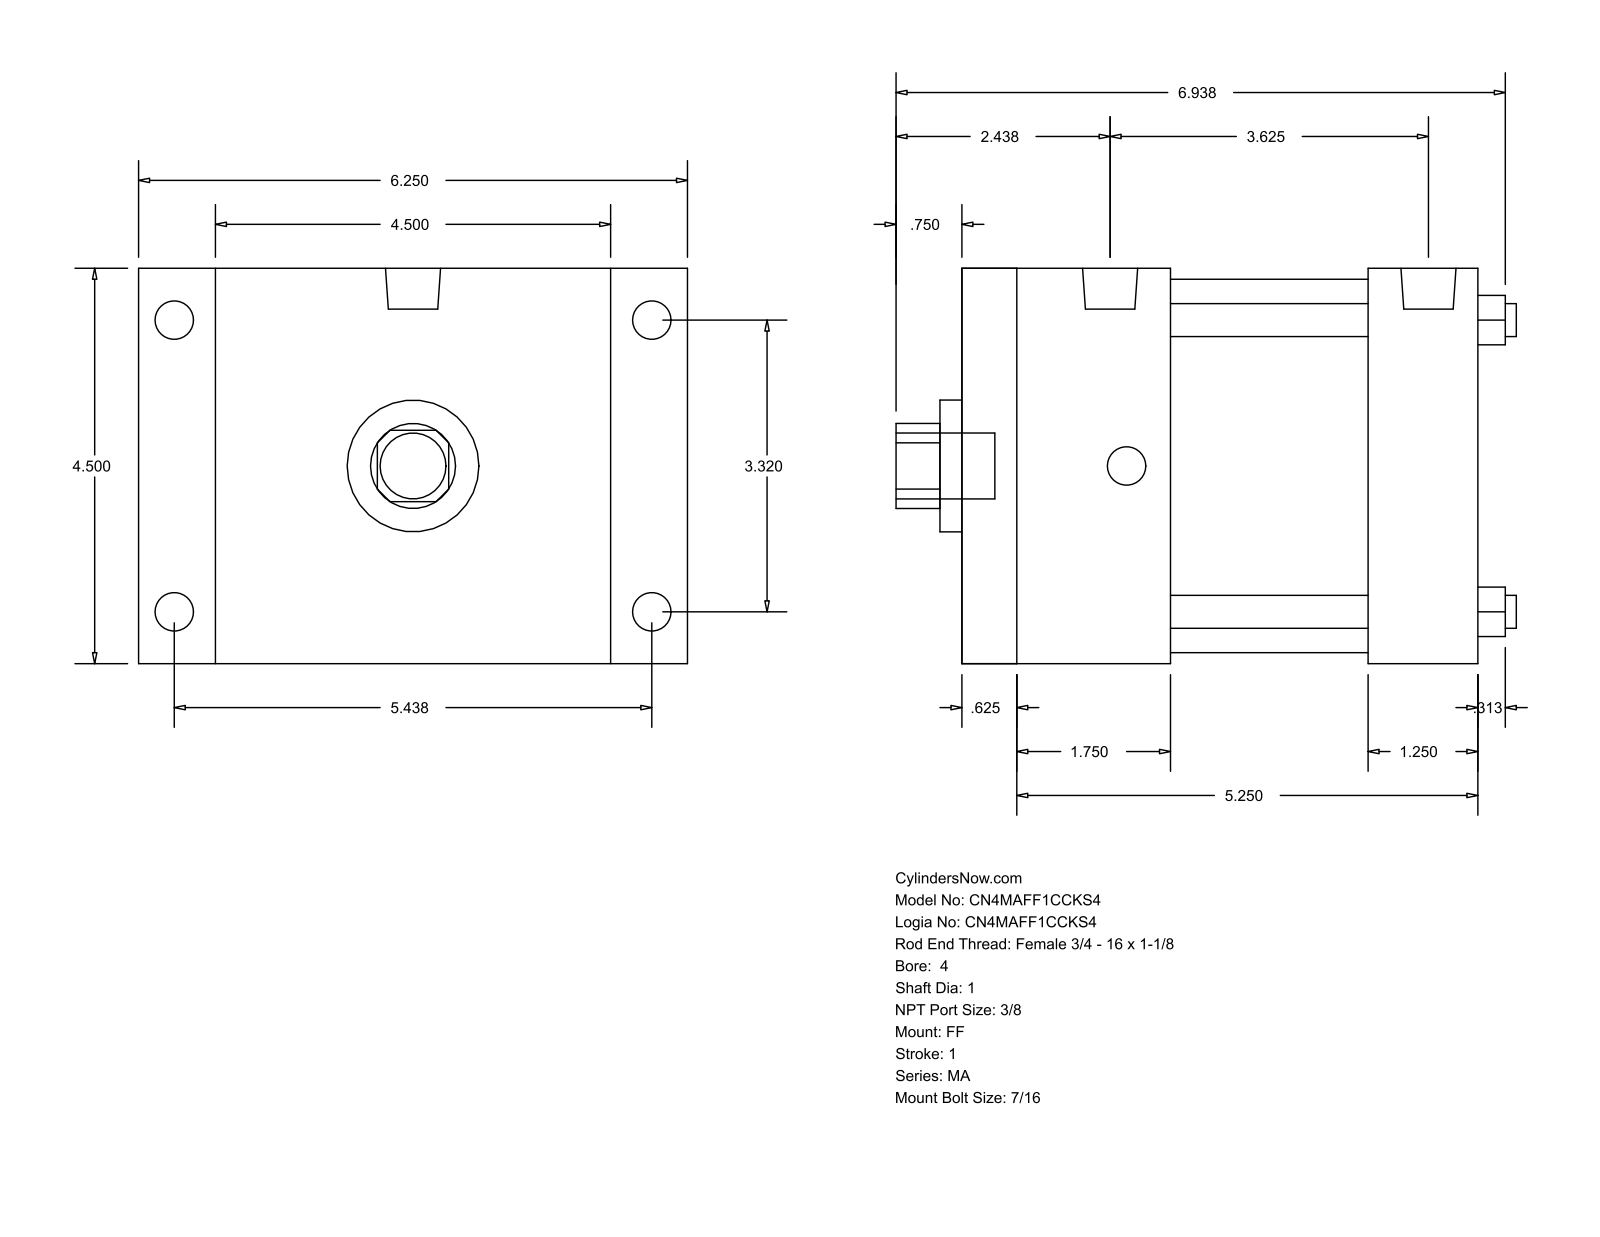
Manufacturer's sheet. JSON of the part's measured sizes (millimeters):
{"part_name": "MA_FF__0400_1", "step_written_by": "GSSL Pune (CONFIG_CONTROL_DESIGN)", "units": "millimeters", "bodies": {"solids": 0, "faces": 92, "planar": 64, "cylindrical": 28, "other": 0}, "overall_size": [179.39, 158.75, 114.3], "round_holes": [[9.53, 4], [25.4, 1], [38.1, 1], [107.95, 1]], "round_bosses_or_shafts": [[11.11, 8], [15.93, 2], [19.05, 1]], "partial_cylinders_radius": [[12.29, 1]], "face_to_face_distances": [114.3, 149.23, 15.87, 133.36, 136.53, 22.23, 117.48, 101.61, 31.75, 60.33], "hole_center_spacings": [59.62, 84.32, 119.25]}
